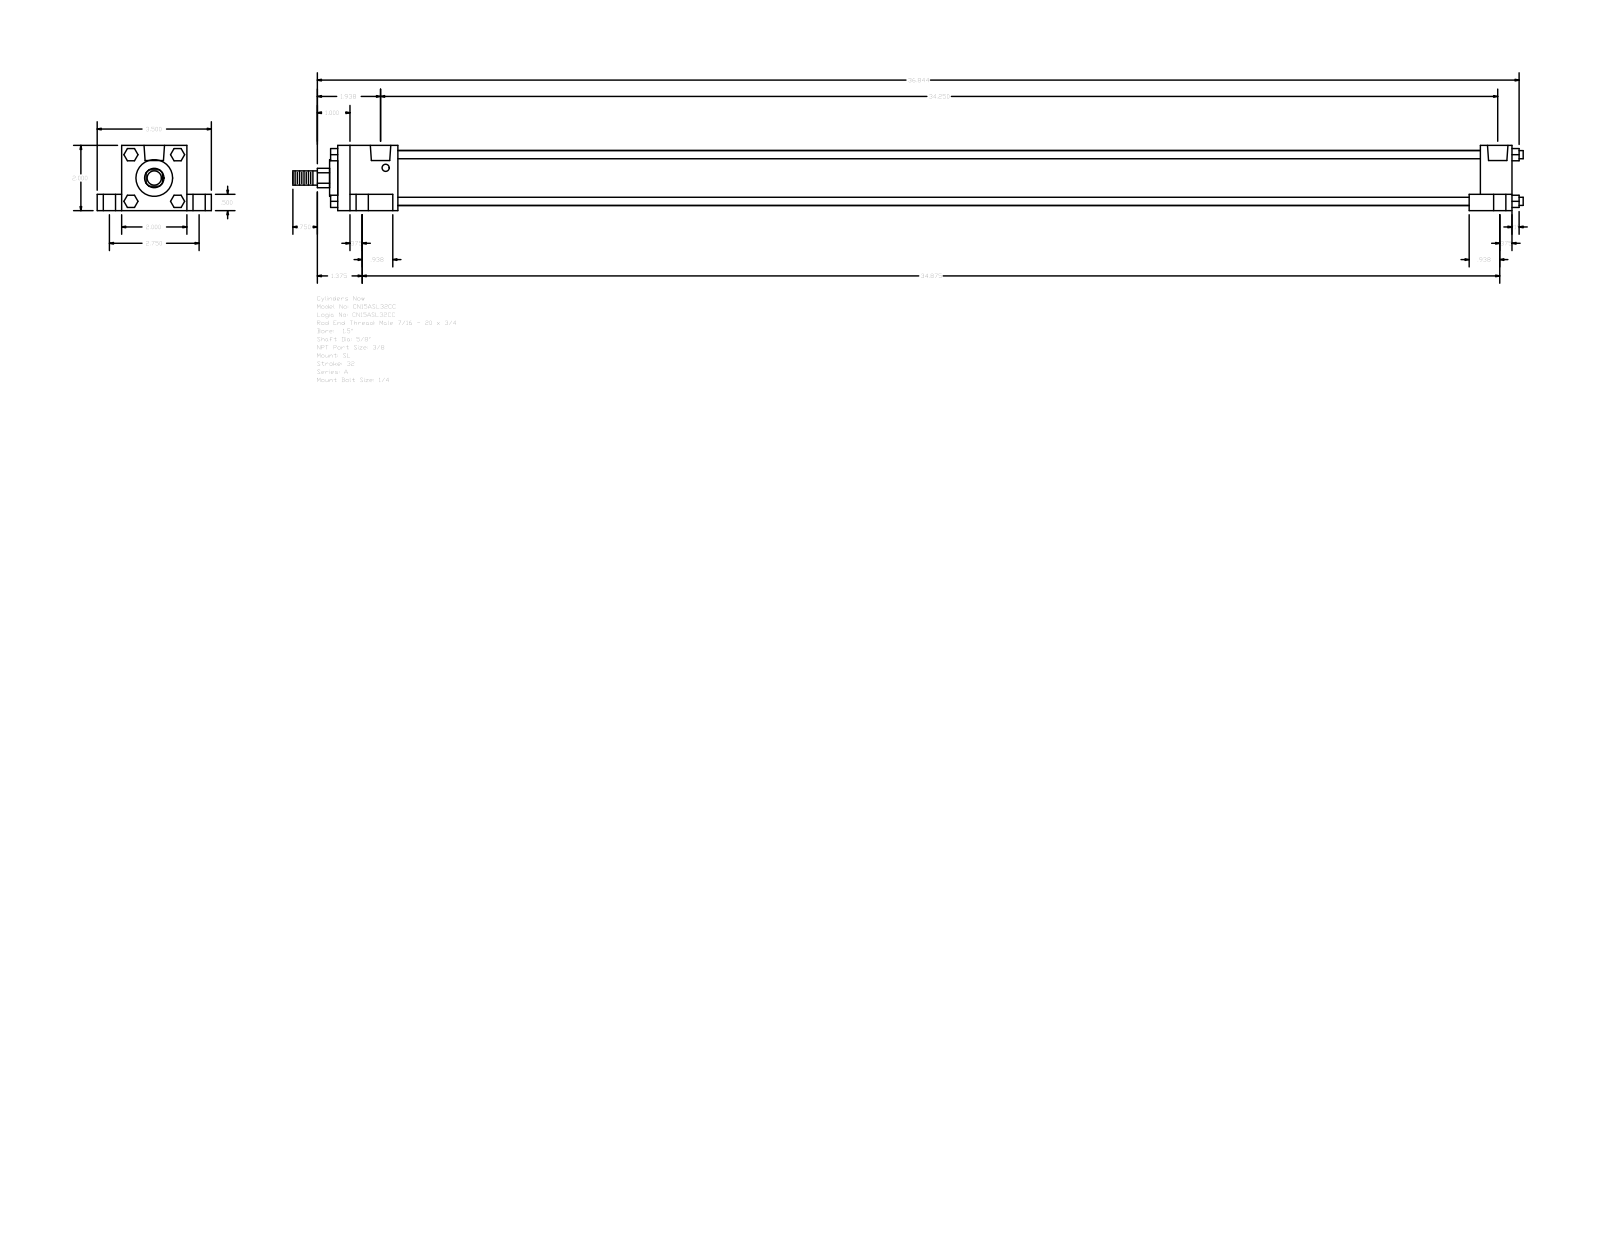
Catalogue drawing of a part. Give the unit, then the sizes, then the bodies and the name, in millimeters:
Units: millimetres
Overall size (bounding box): 958.06 × 88.9 × 50.8
Round holes (diameter × count): ⌀5.56 ×4, ⌀9.53 ×4, ⌀15.88 ×4, ⌀15.93 ×2
Round bosses / shafts (diameter × count): ⌀6.35 ×4, ⌀42.93 ×1, ⌀28.57 ×1, ⌀15.88 ×1, ⌀11.11 ×1
Partial cylindrical surfaces — rounded edges, fillets, slot ends (radius × count): R7.54 ×1
Main face-to-face distances: 50.8, 19.05, 38.1, 12.7, 69.85, 914.39, 9.52, 889.79, 24.6, 46.83
Hole centre spacings: 3.97, 34.96, 35.36, 37.73, 39.41, 69.84, 862.01, 865.98
Bodies: 0 solids, 148 faces (112 planar, 36 cylindrical, 0 other)
Part name (STEP PRODUCT): A_SL__0150_0.625
STEP written by: GSSL Pune (CONFIG_CONTROL_DESIGN)
